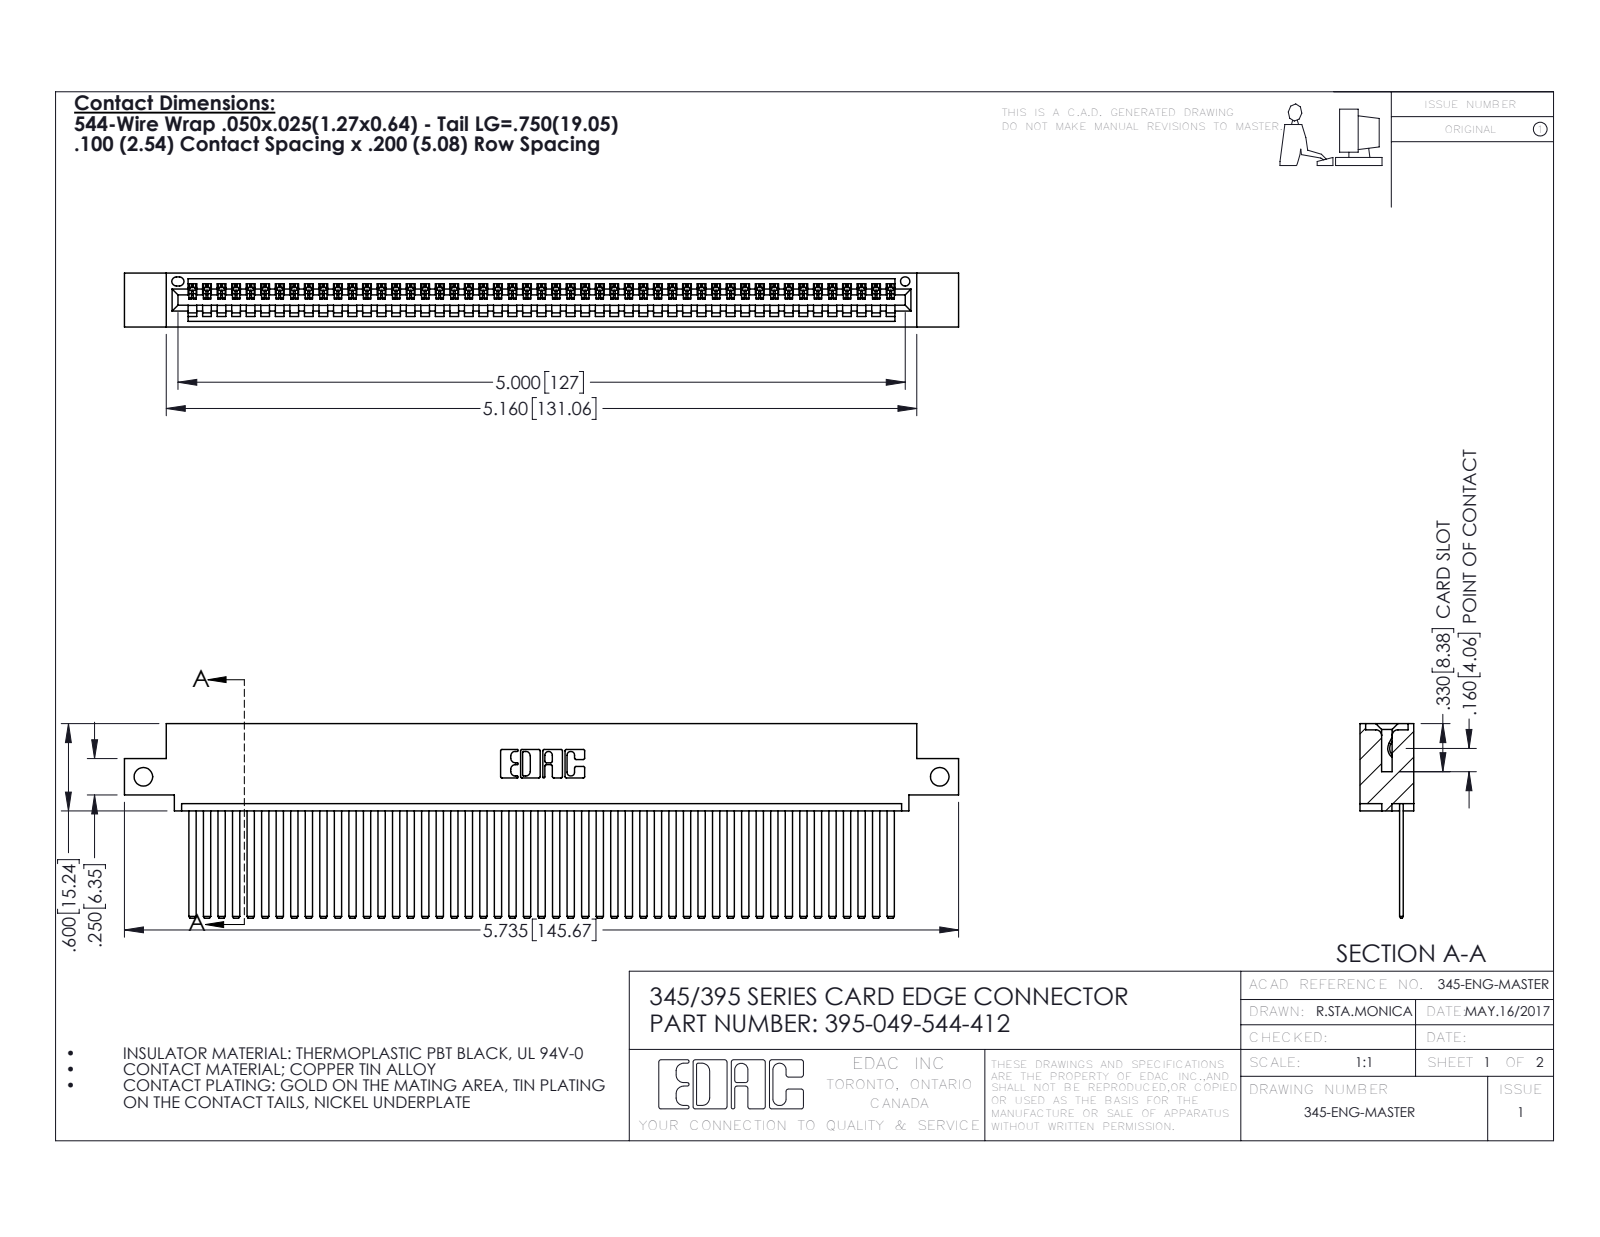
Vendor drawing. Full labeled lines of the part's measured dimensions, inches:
Part name (STEP PRODUCT): 345-292-001_345-293-144; 395-049-544-412; 345 Part_0.110 Offset - Side Mount
STEP written by: SolidWorks 2016 (CONFIG_CONTROL_DESIGN)
Units: inches
Bodies: 50 solids, 2678 faces (1848 planar, 830 cylindrical, 0 other)
Overall size (bounding box): 5.735 × 1.337 × 0.37
Volume: 0.873 in³ · Surface area: 32.15 in²
Round holes (diameter × count): ⌀0.128 ×2, ⌀0.064 ×1
Partial cylindrical surfaces — rounded edges, fillets, slot ends (radius × count): R0.006 ×98, R0.01 ×22, R0.007 ×6, R0.031 ×6, R0.026 ×3, R0.031 ×2, R0.04 ×2, R0.014 ×1
Main face-to-face distances: 0.072, 0.298, 0.025, 0.098, 0.272, 0.37, 0.2, 0.225, 0.149, 0.072
Hole centre spacings: 5.475
